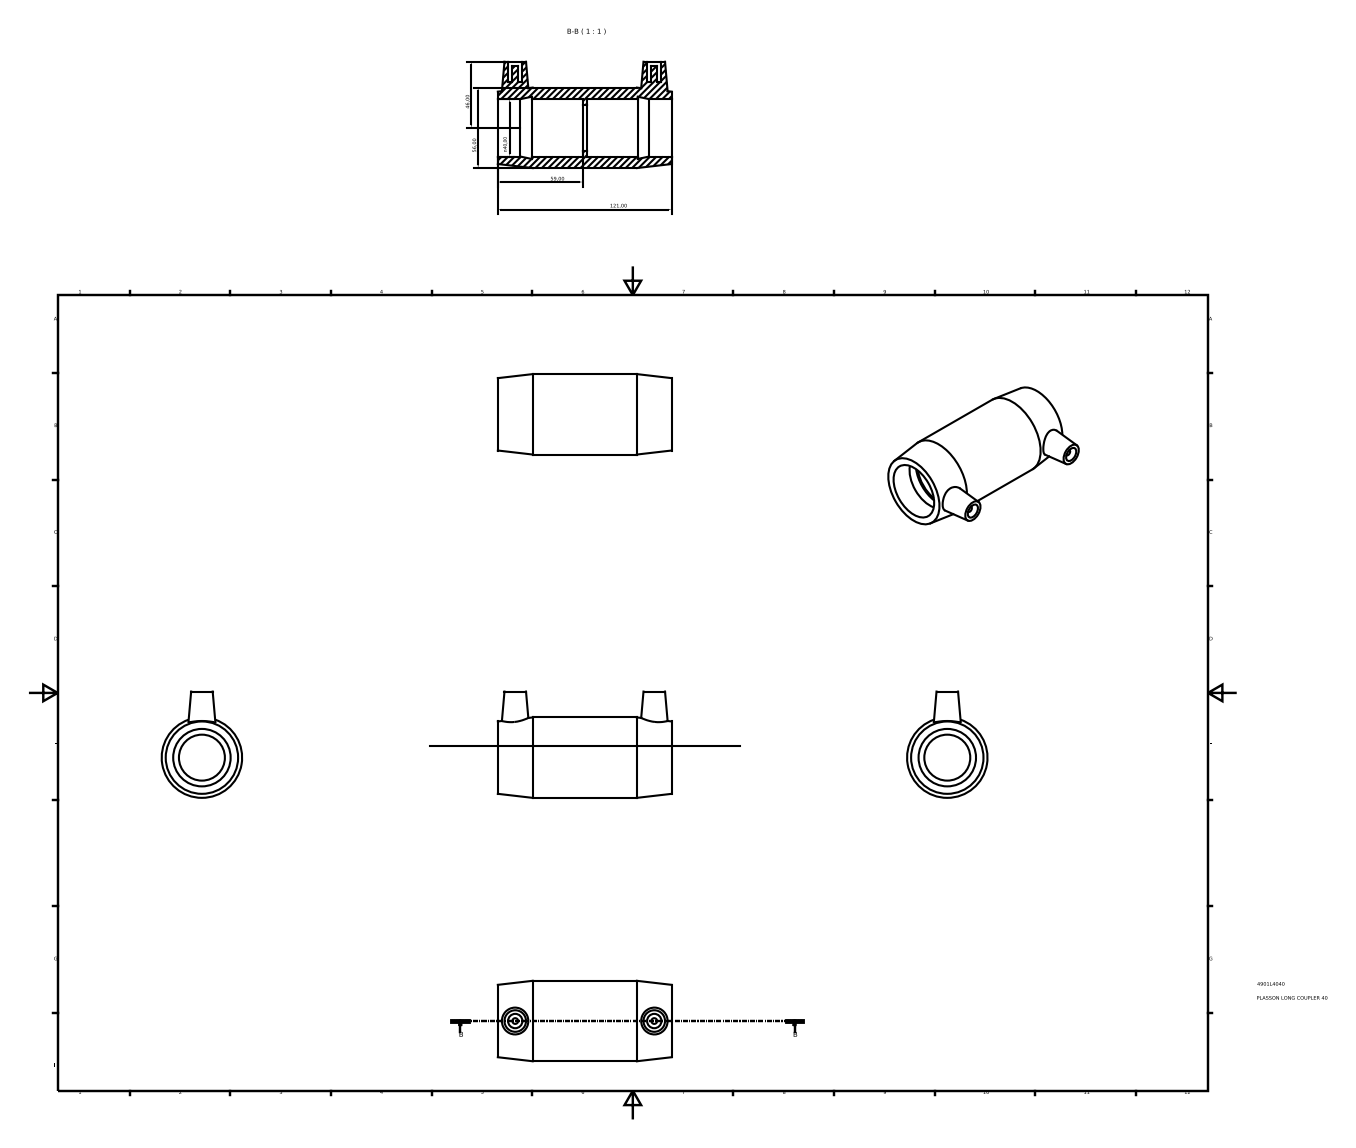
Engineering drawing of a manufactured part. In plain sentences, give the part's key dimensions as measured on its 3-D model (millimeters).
The part is named "4901L4040". Its 3-D file was written by "Autodesk Inventor 2015 (AUTOMOTIVE_DESIGN)". It is 1 solid with 28 faces: 12 planar, 10 cylindrical and 6 other. Overall it measures 121 by 74 by 56 millimeters. Its volume is 140 932 cubic millimeters and its surface area 42 092 square millimeters. Round holes: 2 of diameter 10, 1 of diameter 32, 1 of diameter 40. Round bosses or shafts: 2 of diameter 4, 1 of diameter 56. The main face-to-face distances are 59, 62, 121, 3, 23.6, 97.4, 35.4, 38.4, 73.8, 14. The hole center spacings are 96.8.
